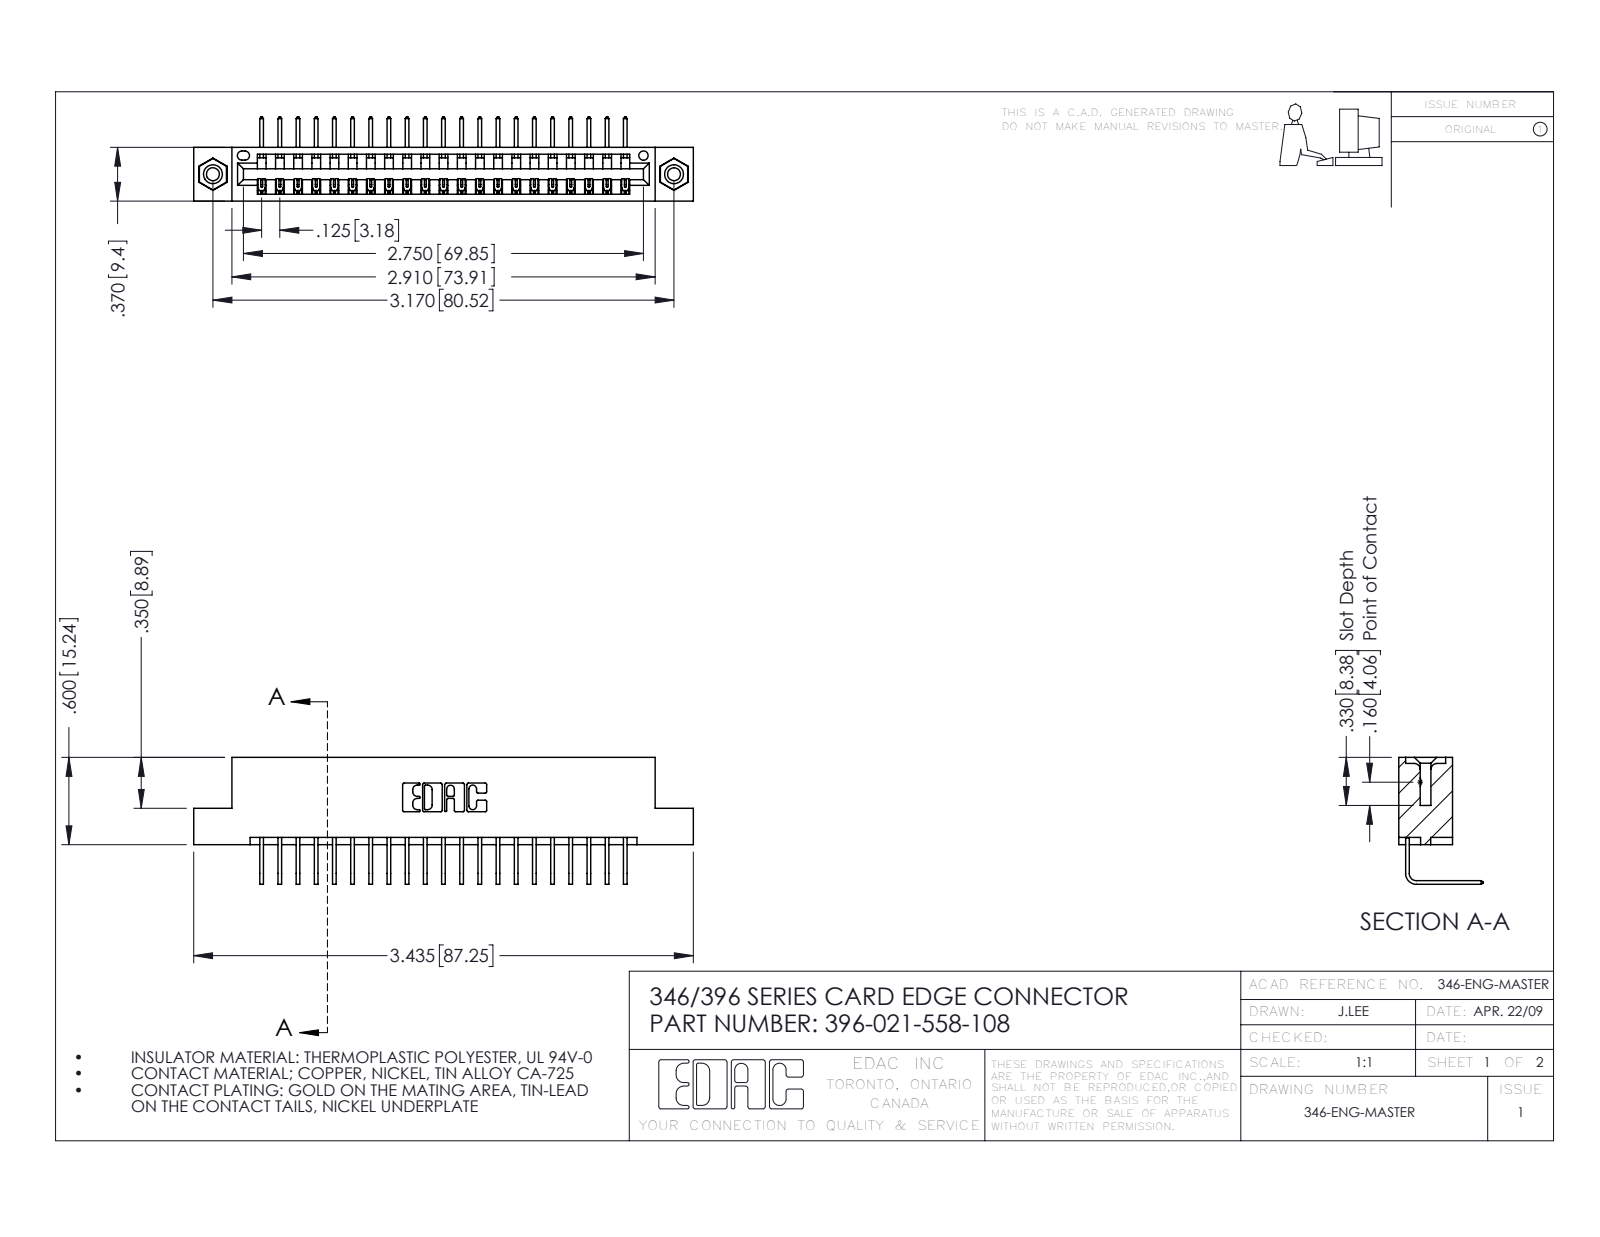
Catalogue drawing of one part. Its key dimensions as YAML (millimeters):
part_name: "345-292-001_558 Tail - 2; 396-021-558-108; 346 Part_Flush Mounting Lugs - 0.156 Dia-TI; 345-250-001_345-250-003-102"
step_written_by: "SolidWorks 2016 (CONFIG_CONTROL_DESIGN)"
units: millimeters
bodies: {solids: 24, faces: 1442, planar: 990, cylindrical: 436, other: 16}
overall_size: [87.2, 22.2, 14.7]
volume: 8280
surface_area: 10550
round_holes:
  - {diameter: 2.3, count: 2}
  - {diameter: 3.2, count: 2}
  - {diameter: 4, count: 2}
  - {diameter: 1.6, count: 1}
round_bosses_or_shafts:
  - {diameter: 3.9, count: 2}
partial_cylinders:
  - {radius: 0.2, count: 42}
  - {radius: 0.3, count: 22}
  - {radius: 0.2, count: 6}
  - {radius: 0.8, count: 6}
  - {radius: 0.7, count: 3}
  - {radius: 0.8, count: 2}
  - {radius: 1, count: 2}
  - {radius: 0.4, count: 1}
face_to_face_distances: [8.2, 1.2, 9.4, 6.4, 7.6, 0.6, 1.8, 3.8, 5.6, 2.5]
hole_center_spacings: [6.2, 75.3, 80.5]
